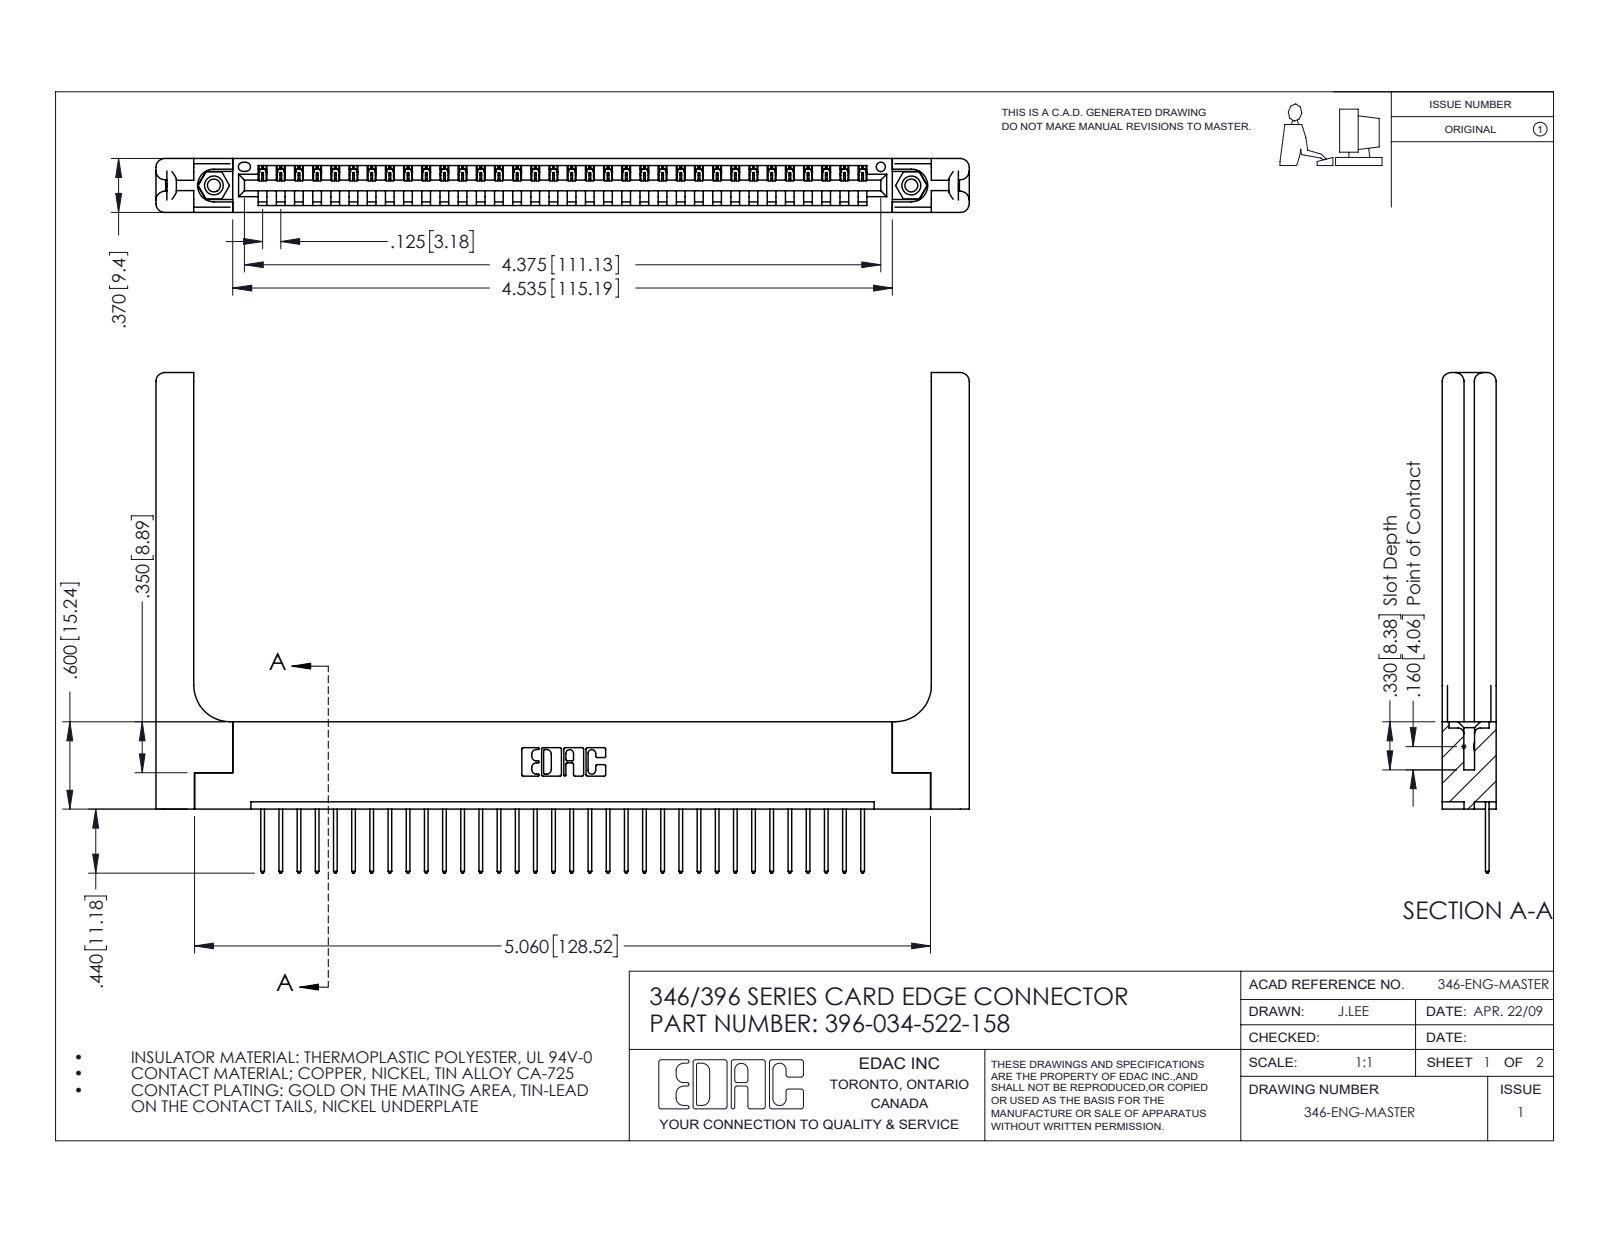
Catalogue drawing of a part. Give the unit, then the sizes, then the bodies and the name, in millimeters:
Units: millimetres
Overall size (bounding box): 142 × 87.4 × 9.4
Round holes (diameter × count): ⌀2.3 ×2, ⌀3.2 ×2, ⌀4 ×2, ⌀1.6 ×1
Round bosses / shafts (diameter × count): ⌀3.9 ×2
Partial cylindrical surfaces — rounded edges, fillets, slot ends (radius × count): R0.2 ×68, R0.3 ×68, R0.3 ×22, R1.5 ×16, R0.2 ×6, R0.8 ×6, R0.7 ×3, R0.8 ×2
Main face-to-face distances: 9.4, 1.2, 8.2, 1.8, 3.8, 3.8, 6.4, 7.6, 0.6, 5.6
Hole centre spacings: 6.2, 116.5, 121.8
Volume: 21 060 mm³ · Surface area: 22 140 mm²
Bodies: 39 solids, 2350 faces (1584 planar, 706 cylindrical, 60 other)
Part name (STEP PRODUCT): 345-250-001_345-250-001-102; 396-034-522-158; 346 Part_Flush Mounting Lugs - 0.156 Dia-TH; 346-220-058_345-220-058 (+1 more)
STEP written by: SolidWorks 2016 (CONFIG_CONTROL_DESIGN)
